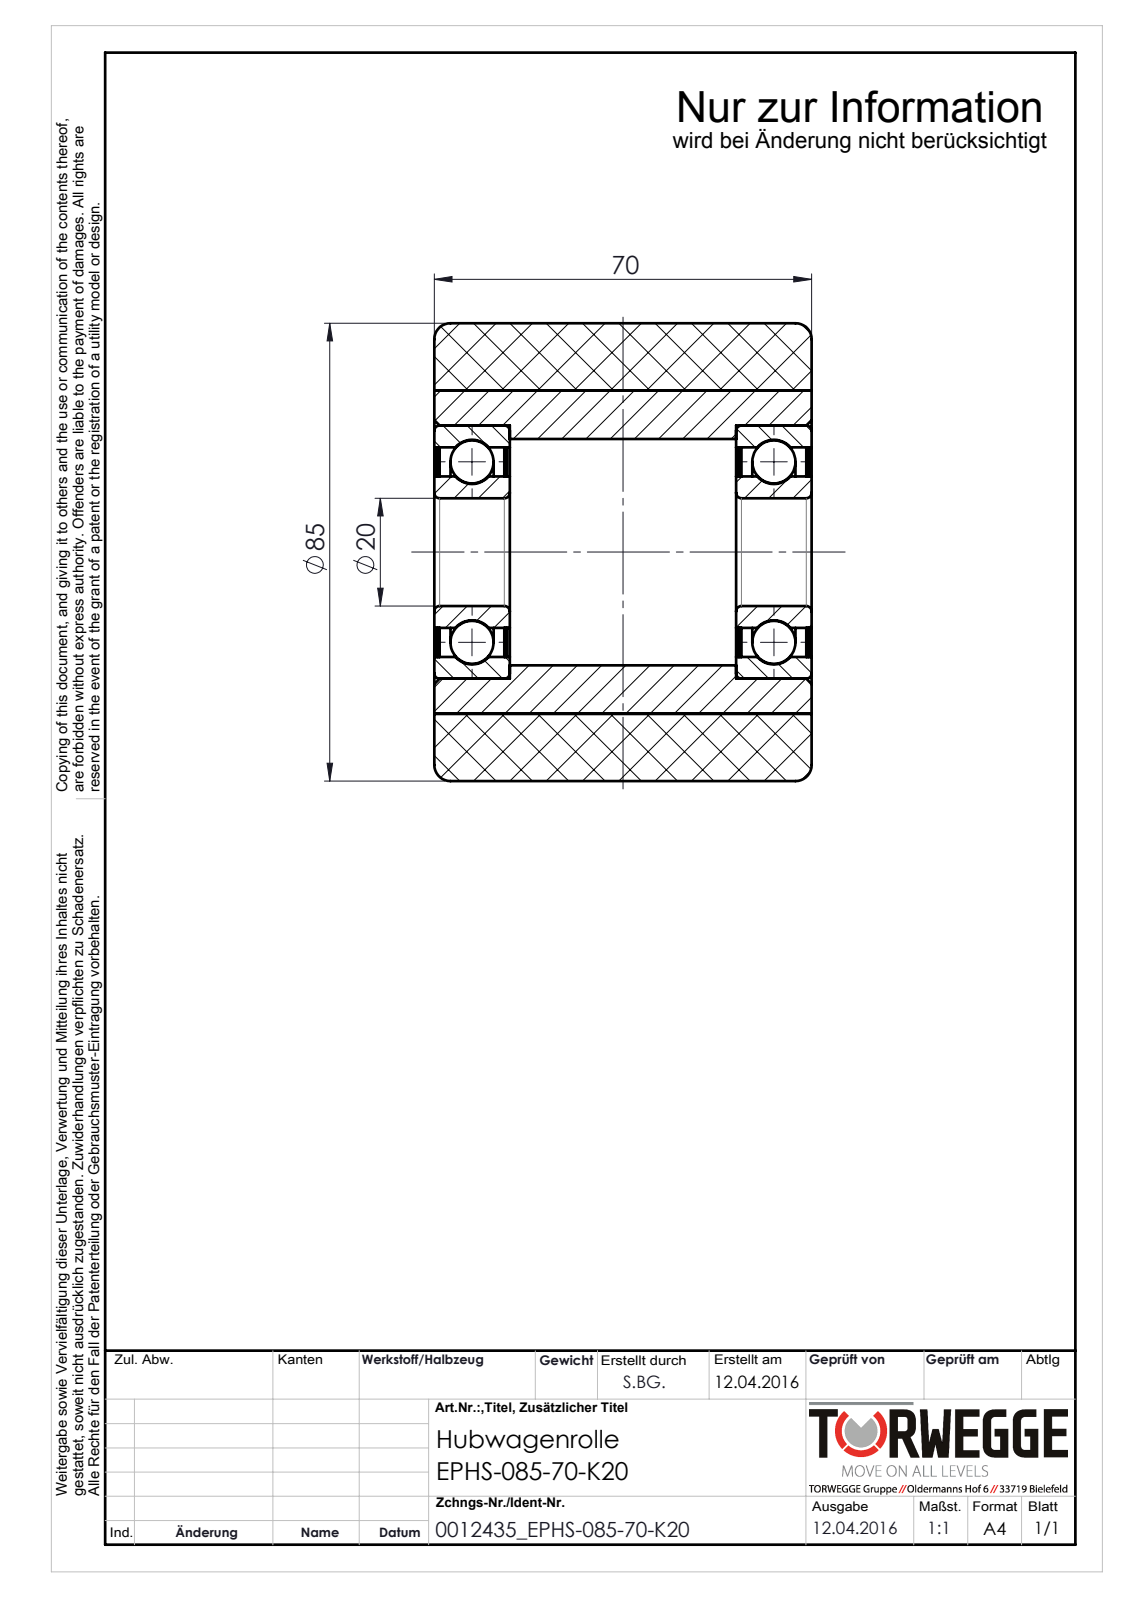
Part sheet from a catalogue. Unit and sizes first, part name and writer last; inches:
Units: inches
Overall size (bounding box): 3.346 × 3.346 × 2.756
Round holes (diameter × count): ⌀0.787 ×1, ⌀1.106 ×1, ⌀1.531 ×1, ⌀1.654 ×1, ⌀1.85 ×1, ⌀2.362 ×1
Round bosses / shafts (diameter × count): ⌀3.346 ×1
Main face-to-face distances: 0.02, 2.205, 2.756, 0.512, 0.039, 0.531, 2.224, 2.185, 0.492, 0.551
Volume: 19.66 in³ · Surface area: 136.3 in²
Bodies: 12 solids, 118 faces (22 planar, 52 cylindrical, 44 other)
Part name (STEP PRODUCT): 0012435_EPHS-085-70-K20
STEP written by: SolidWorks 2016 (AUTOMOTIVE_DESIGN)
